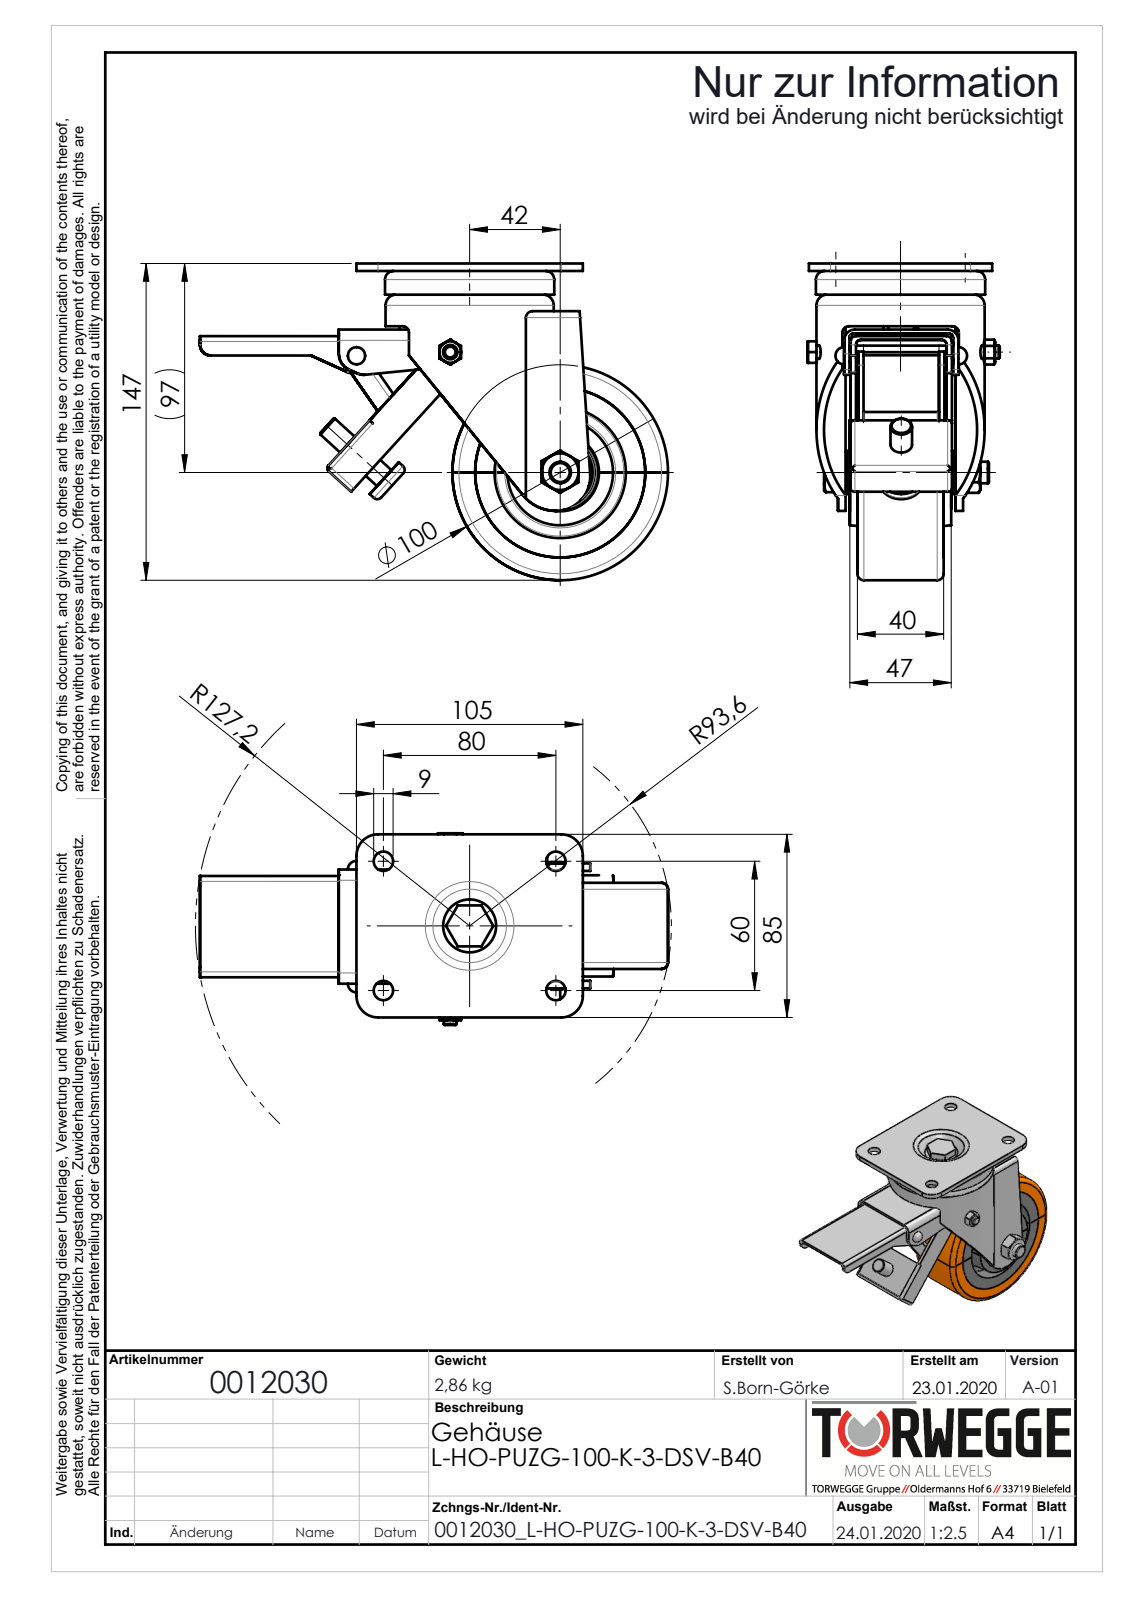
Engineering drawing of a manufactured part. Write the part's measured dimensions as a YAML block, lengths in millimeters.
part_name: "0012030_L-HO-PUZG-100-K-3-DSV-B40_(A-01)"
step_written_by: "SolidWorks 2018 (AUTOMOTIVE_DESIGN)"
units: millimeters
bodies: {solids: 0, faces: 855, planar: 224, cylindrical: 220, other: 411}
overall_size: [217.05, 147, 89]
round_holes:
  - {diameter: 9, count: 4}
  - {diameter: 8.5, count: 2}
  - {diameter: 5.35, count: 1}
  - {diameter: 6, count: 1}
  - {diameter: 6.5, count: 1}
  - {diameter: 10.2, count: 1}
  - {diameter: 10.3, count: 1}
  - {diameter: 14, count: 1}
  - {diameter: 15, count: 1}
  - {diameter: 16, count: 1}
  - {diameter: 16.3, count: 1}
  - {diameter: 16.5, count: 1}
round_bosses_or_shafts:
  - {diameter: 10, count: 3}
  - {diameter: 20, count: 2}
  - {diameter: 100, count: 1}
  - {diameter: 78.5, count: 1}
  - {diameter: 78, count: 1}
  - {diameter: 71, count: 1}
  - {diameter: 67.5, count: 1}
  - {diameter: 65.4, count: 1}
partial_cylinders:
  - {radius: 2, count: 5}
  - {radius: 2.25, count: 4}
  - {radius: 2.5, count: 4}
  - {radius: 3, count: 4}
  - {radius: 10, count: 4}
  - {radius: 4, count: 3}
  - {radius: 5, count: 3}
  - {radius: 6, count: 3}
face_to_face_distances: [5.5, 3, 3.5, 49, 3.47, 2.5, 45.5, 1.74, 93.53, 97]
hole_center_spacings: [50, 60, 80, 100, 0.38, 41.84, 75.37, 75.65]
